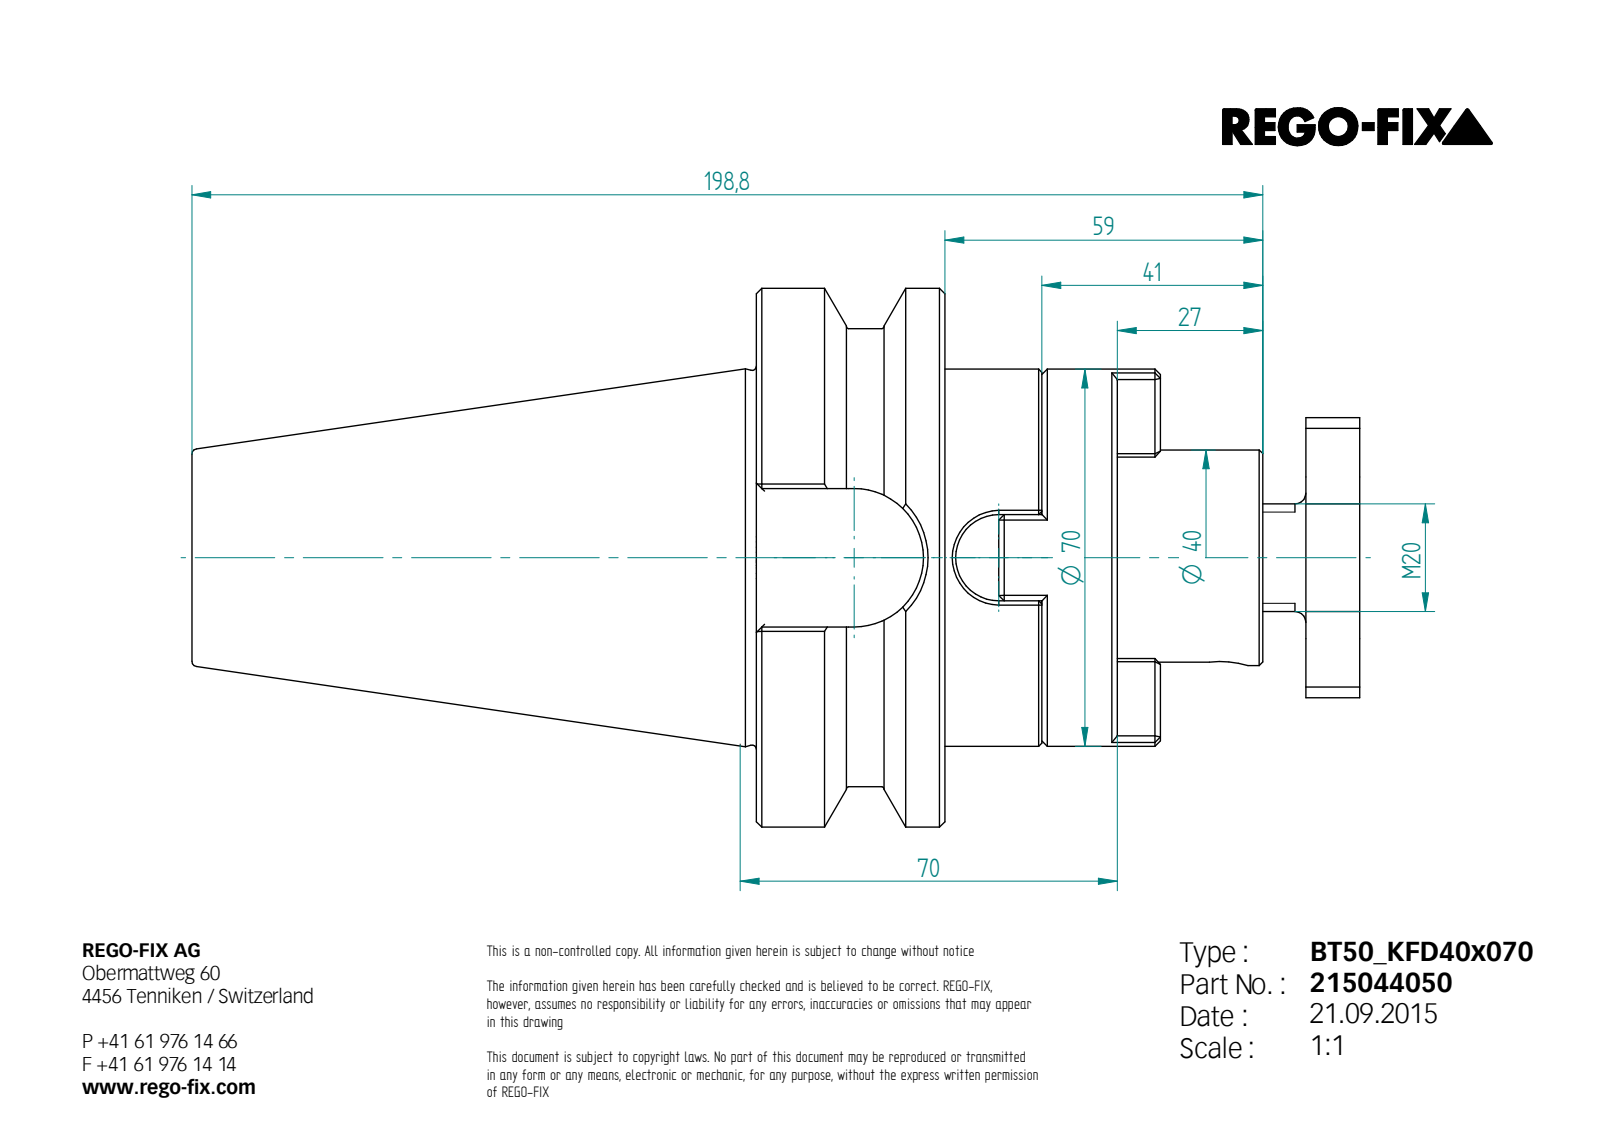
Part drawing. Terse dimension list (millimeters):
written by: Unknown (AUTOMOTIVE_DESIGN)
unit: mm
bodies: 3 solids, 207 faces (118 planar, 35 cylindrical, 54 other)
size: 216.8 × 100 × 100
volume: 611 354 mm³; area: 84 854 mm²
holes: 1× ⌀17.29, 1× ⌀20.75, 1× ⌀21, 1× ⌀25, 1× ⌀40
bosses: 1× ⌀100, 1× ⌀85, 1× ⌀70, 1× ⌀39.4, 1× ⌀20
rounds: 6× R5, 4× R0.5, 1× R8, 1× R12.85, 1× R26
face distances: 18, 35, 67, 53, 59, 45, 32, 14, 10, 112
